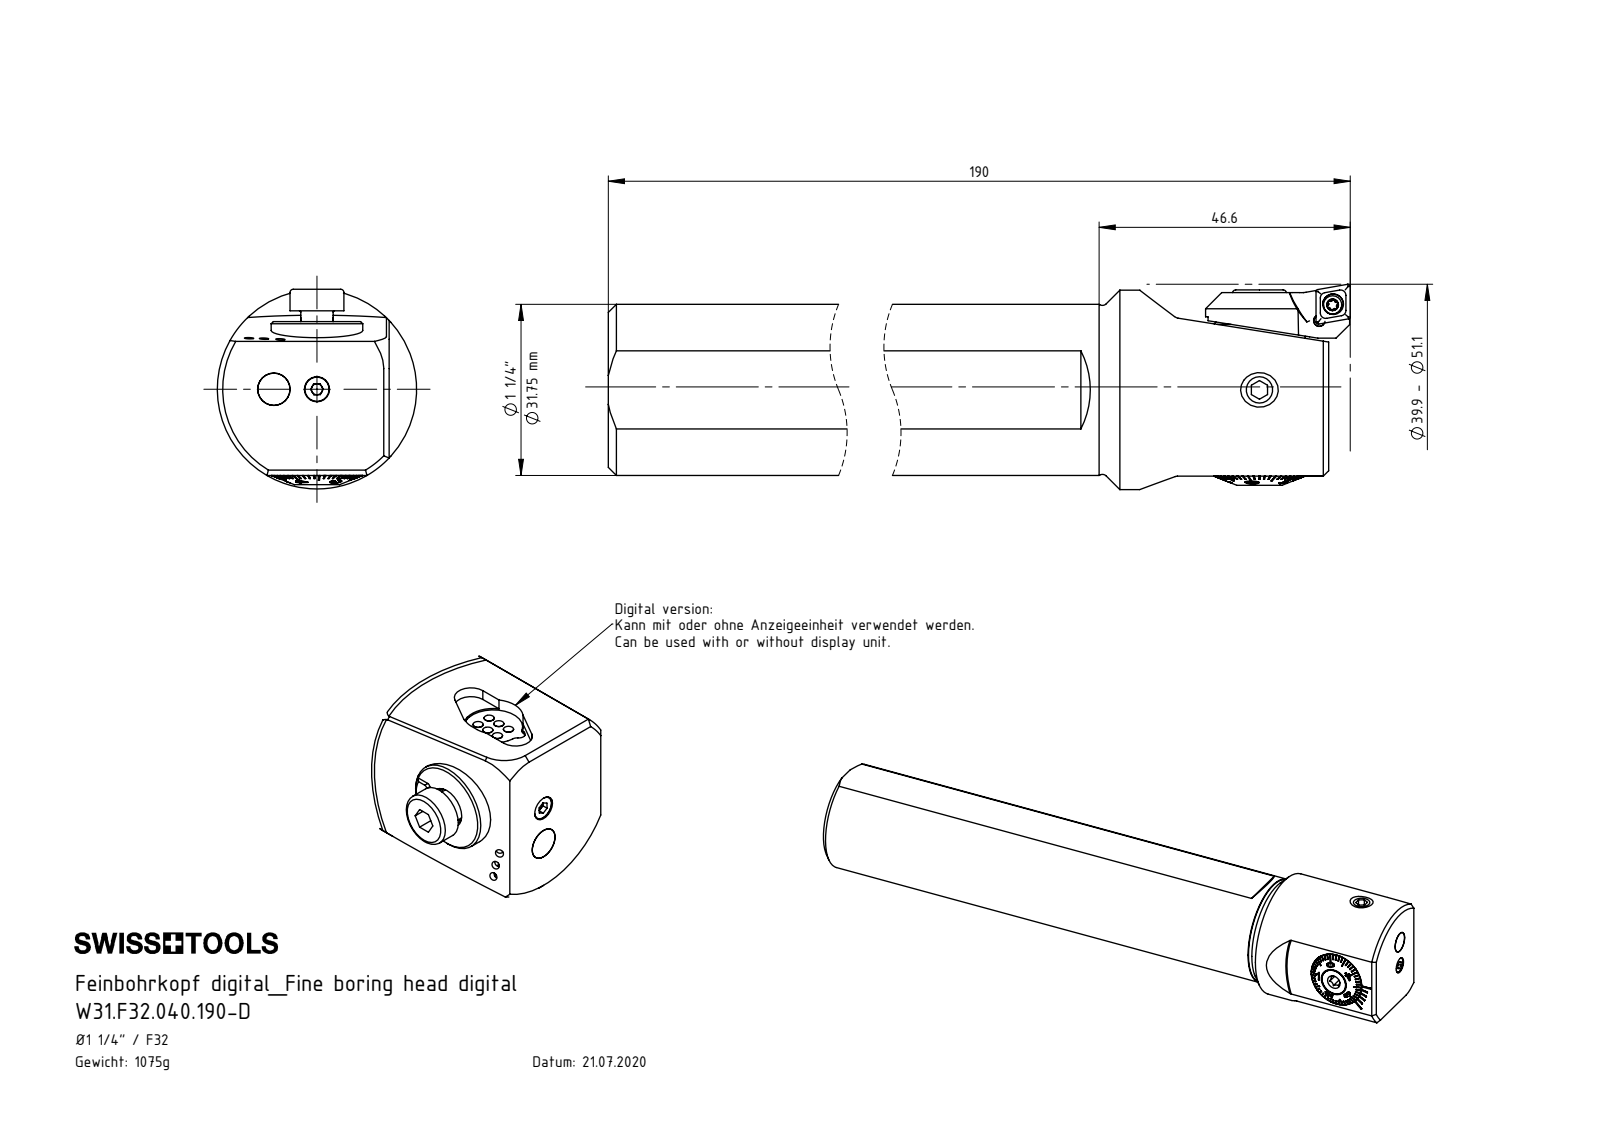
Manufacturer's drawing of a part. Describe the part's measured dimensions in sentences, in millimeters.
The part is named "DIN 3771 - 15x1.0; F32-BG2.014.012_A; Klebstoff D6; F32-BG1.010.006_A (+8 more)". Its 3-D file was written by "SolidWorks 2022 (CONFIG_CONTROL_DESIGN)". It is 18 solids with 927 faces: 440 planar, 183 cylindrical and 304 other. Overall it measures 190 by 38.1 by 37 millimeters. Its volume is 139 444 cubic millimeters and its surface area 35 218 square millimeters. Round holes: 3 of diameter 1.5, 2 of diameter 2.05, 2 of diameter 3.3, 2 of diameter 5, 2 of diameter 8.5, 1 of diameter 2.1, 1 of diameter 2.7, 1 of diameter 2.8, 1 of diameter 2.9, 1 of diameter 3, 1 of diameter 3.85, 1 of diameter 4.2. Round bosses or shafts: 6 of diameter 1.9, 2 of diameter 6, 2 of diameter 2.5, 1 of diameter 37, 1 of diameter 31.75, 1 of diameter 16.98, 1 of diameter 16.85, 1 of diameter 14.65. Partial cylindrical surfaces (rounded edges, fillets, slot ends): 6 of radius 0.21, 5 of radius 0.5, 4 of radius 0.36, 4 of radius 1.4, 3 of radius 1.1, 3 of radius 1.2, 2 of radius 0.36, 2 of radius 1.75. The main face-to-face distances are 186, 27.52, 4.5, 24.05, 28.55, 0.8, 27.75, 3.7, 1.5, 6.75. The hole center spacings are 1.52, 3.84, 4, 8, 8.72, 10.24.
